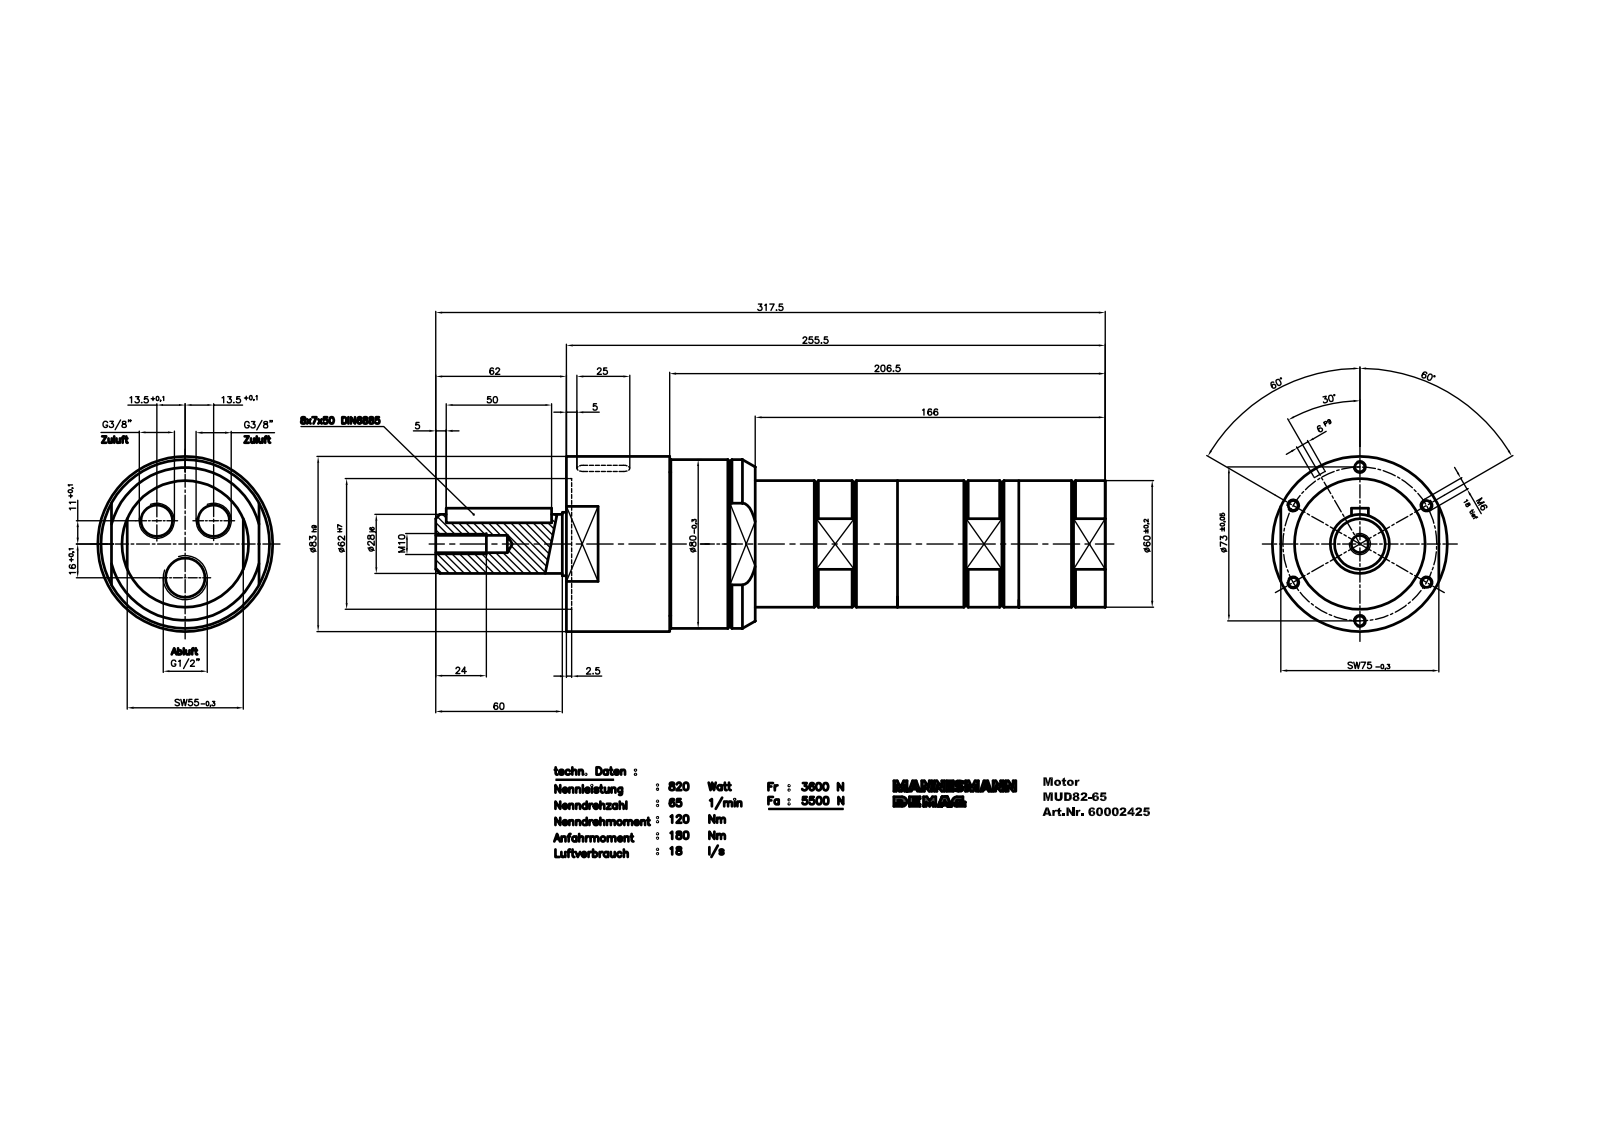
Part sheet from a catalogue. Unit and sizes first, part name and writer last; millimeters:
Units: millimetres
Overall size (bounding box): 317.5 × 83 × 83
Round holes (diameter × count): ⌀1.55 ×2, ⌀5.5 ×2, ⌀38 ×1, ⌀58.69 ×1, ⌀62 ×1
Round bosses / shafts (diameter × count): ⌀5 ×2, ⌀83 ×1, ⌀80 ×1, ⌀74.86 ×1, ⌀60 ×1, ⌀45 ×1, ⌀30 ×1, ⌀28 ×1
Partial cylindrical surfaces — rounded edges, fillets, slot ends (radius × count): R2.25 ×2, R3 ×2, R4 ×2, R7.5 ×2, R8.5 ×1, R23.5 ×1, R29.61 ×1, R32.5 ×1
Main face-to-face distances: 255.5, 89.5, 166, 55, 5, 239.05, 149.55, 16.45, 49, 206.5
Hole centre spacings: 1.53
Volume: 938 208 mm³ · Surface area: 81 073 mm²
Bodies: 1 solid, 230 faces (121 planar, 49 cylindrical, 60 other)
Part name (STEP PRODUCT): MUD 82-65_60002425
STEP written by: Autodesk Inventor 2008 (CONFIG_CONTROL_DESIGN)
